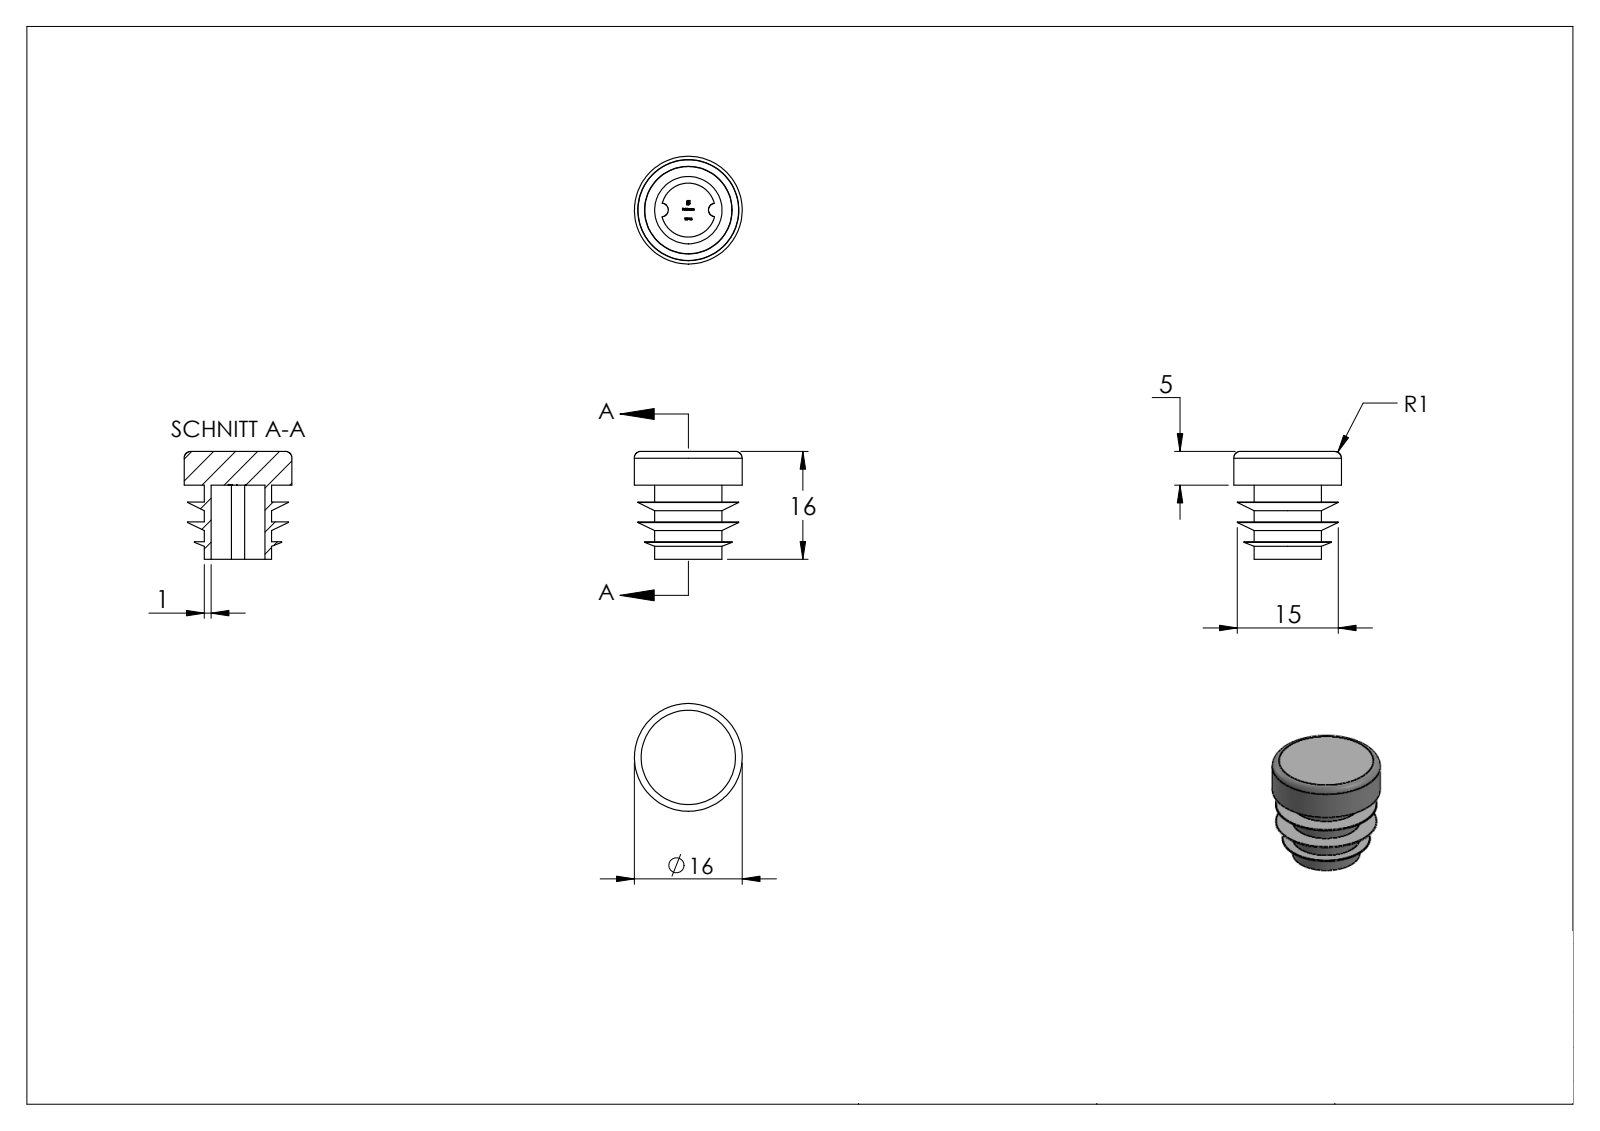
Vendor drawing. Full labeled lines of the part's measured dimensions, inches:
Part name (STEP PRODUCT): 177-16
STEP written by: SolidWorks 2018 (CONFIG_CONTROL_DESIGN)
Units: inches
Bodies: 1 solid, 224 faces (131 planar, 9 cylindrical, 84 other)
Overall size (bounding box): 0.63 × 0.63 × 0.63
Volume: 0.091 in³ · Surface area: 2.644 in²
Round holes (diameter × count): ⌀0.315 ×1
Round bosses / shafts (diameter × count): ⌀0.63 ×1, ⌀0.394 ×1
Partial cylindrical surfaces — rounded edges, fillets, slot ends (radius × count): R0.039 ×2
Main face-to-face distances: 0.197, 0.116, 0.215, 0.411, 0.098, 0.295, 0.232, 0.331, 0.528, 0.102
